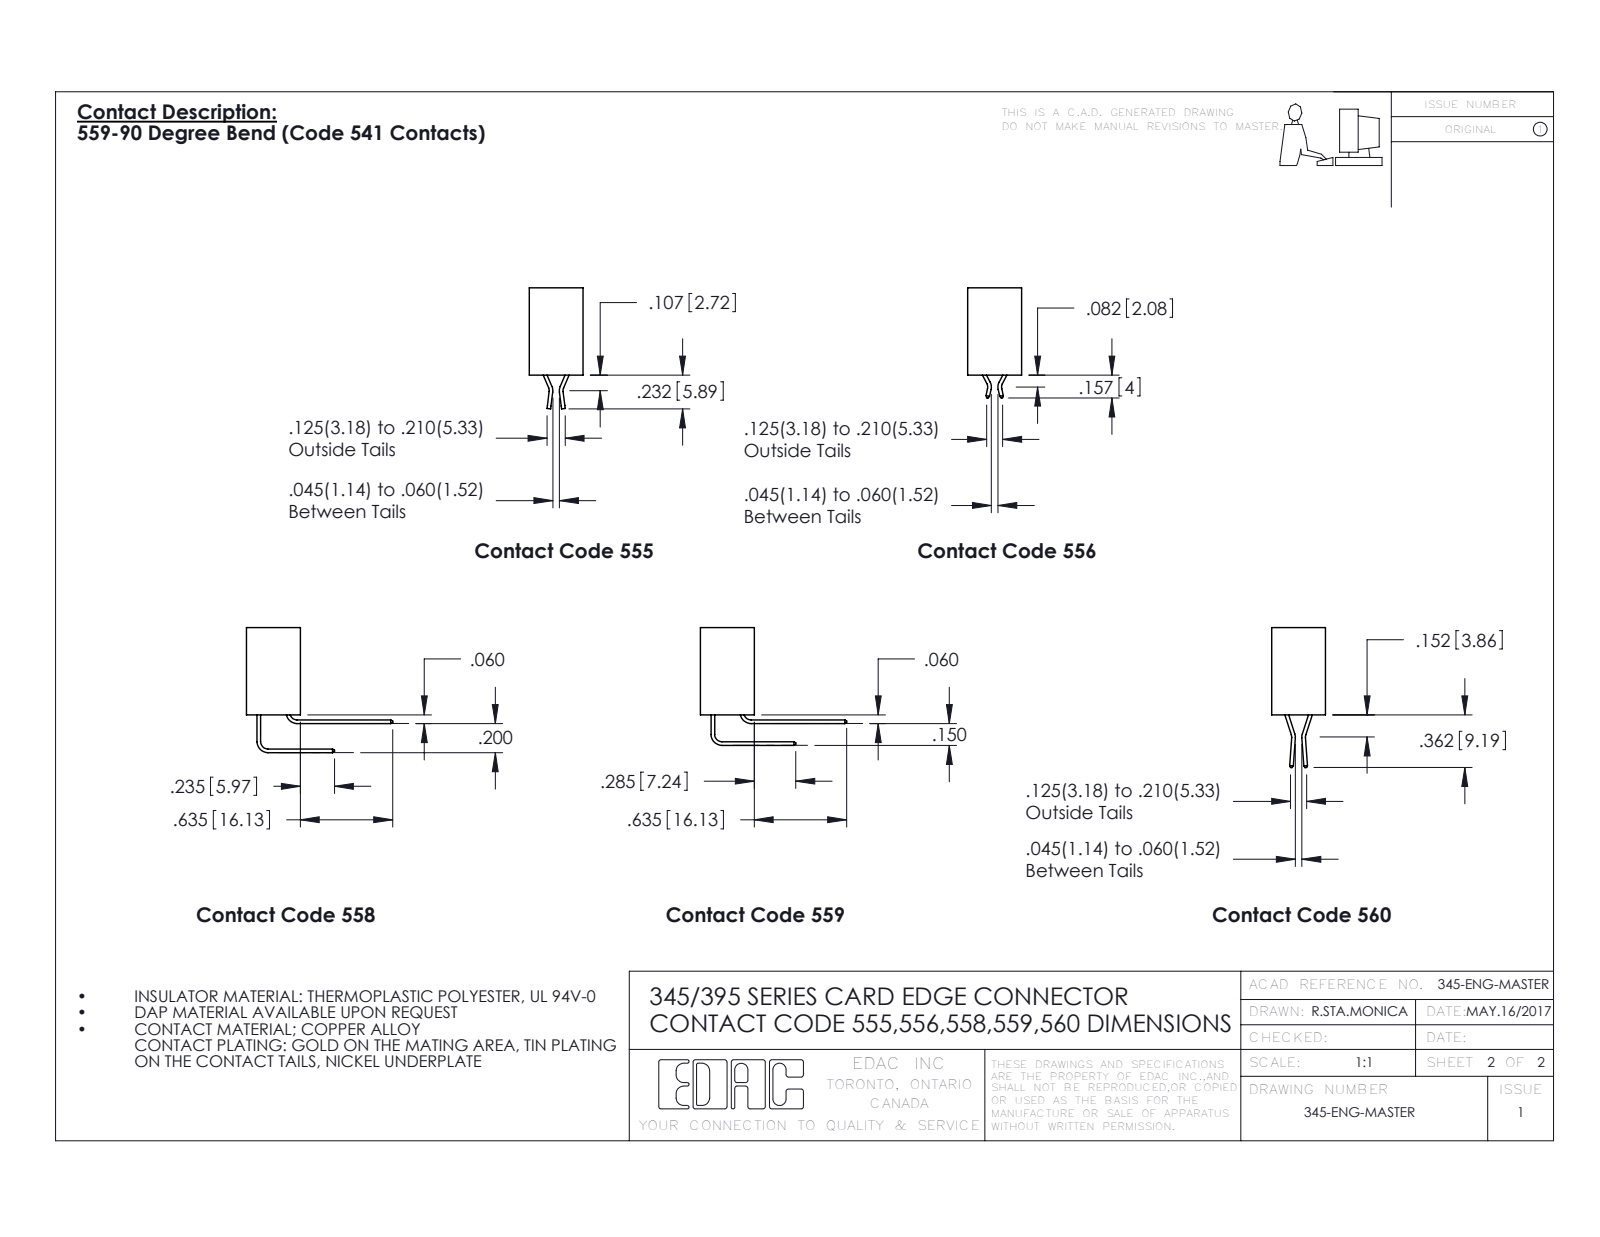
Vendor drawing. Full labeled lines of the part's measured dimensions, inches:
Part name (STEP PRODUCT): 395-022-524-101; 345 Part_No Mounting Lugs; 345-292-001_345-293-124
STEP written by: SolidWorks 2016 (CONFIG_CONTROL_DESIGN)
Units: inches
Bodies: 23 solids, 1482 faces (1088 planar, 394 cylindrical, 0 other)
Overall size (bounding box): 2.46 × 0.762 × 0.37
Volume: 0.383 in³ · Surface area: 12.35 in²
Round holes (diameter × count): ⌀0.064 ×1
Partial cylindrical surfaces — rounded edges, fillets, slot ends (radius × count): R0.006 ×44, R0.01 ×22, R0.007 ×6, R0.031 ×6, R0.026 ×3, R0.031 ×2, R0.04 ×2, R0.014 ×1
Main face-to-face distances: 0.298, 0.072, 0.2, 0.37, 0.098, 0.272, 0.025, 0.225, 0.1, 0.072
